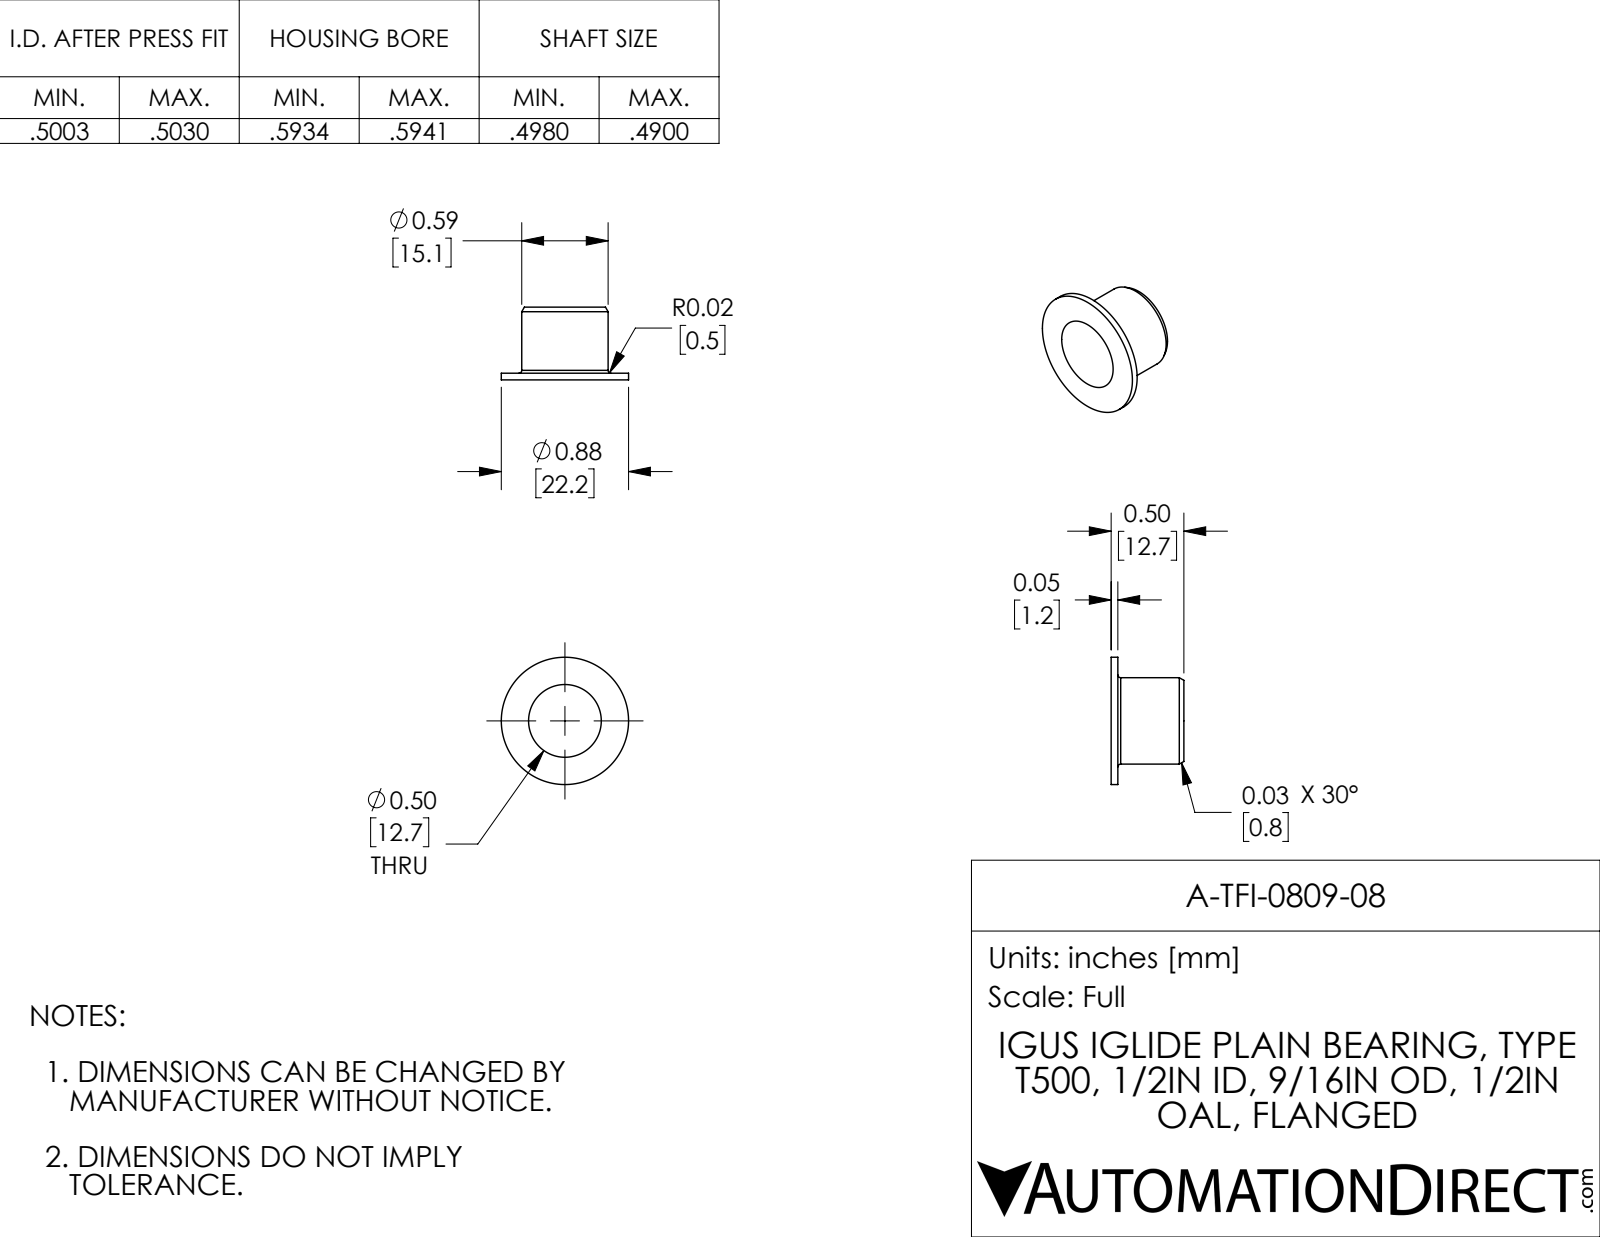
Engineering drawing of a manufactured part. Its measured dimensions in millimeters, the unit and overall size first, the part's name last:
Units: millimetres
Overall size (bounding box): 22.2 × 22.2 × 12.7
Round holes (diameter × count): ⌀12.7 ×1
Round bosses / shafts (diameter × count): ⌀22.2 ×1, ⌀15.1 ×1
Main face-to-face distances: 1.2, 12.7, 11.5
Volume: 900 mm³ · Surface area: 1 630 mm²
Bodies: 1 solid, 13 faces (3 planar, 6 cylindrical, 4 other)
Part name (STEP PRODUCT): A-TFI-0809-08
STEP written by: SolidWorks 2017 (AUTOMOTIVE_DESIGN)
